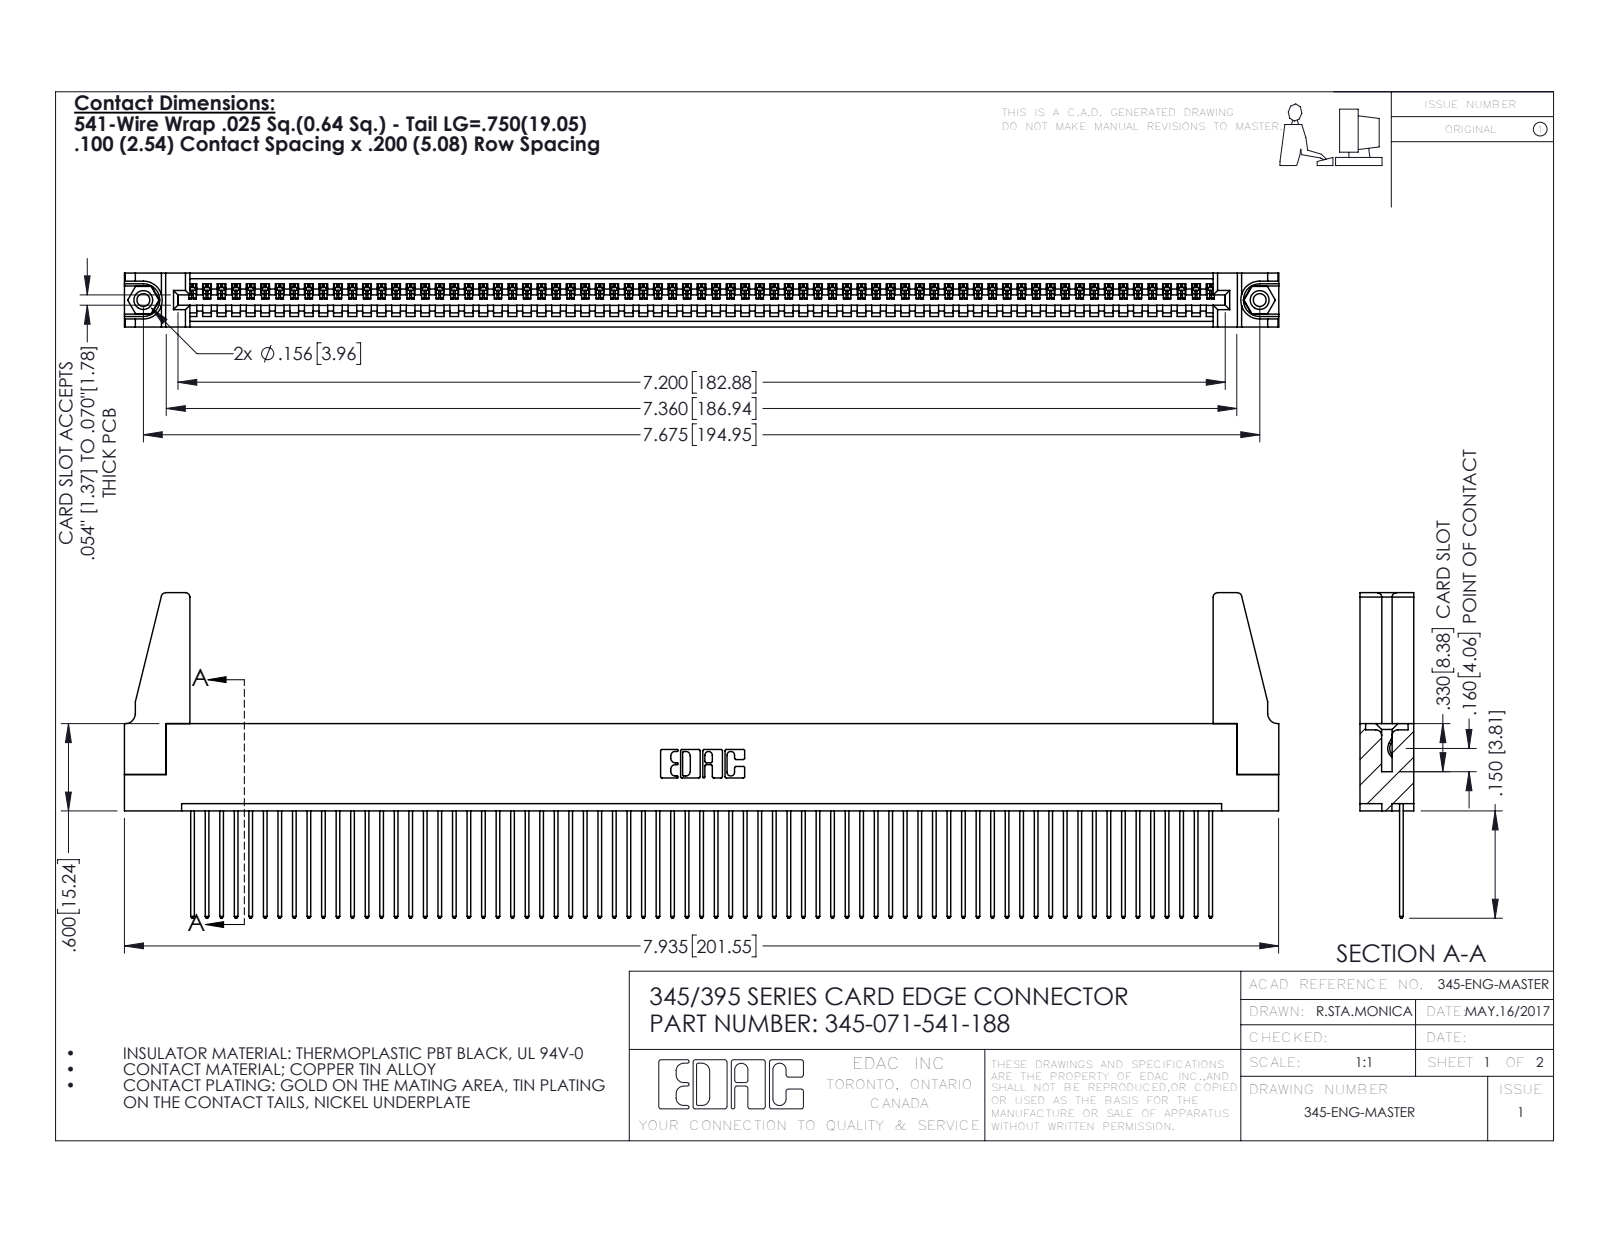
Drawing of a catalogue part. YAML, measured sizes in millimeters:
part_name: "345-071-541-188; 345 Part_Flush Mounting Lugs - 0.156 Dia-TH; 345-250-001_345-250-001-102; 345-292-001_345-293-141 (+1 more)"
step_written_by: "SolidWorks 2016 (CONFIG_CONTROL_DESIGN)"
units: millimeters
bodies: {solids: 76, faces: 4368, planar: 2992, cylindrical: 1360, other: 16}
overall_size: [201.6, 56.8, 9.4]
volume: 22880
surface_area: 30970
round_holes:
  - {diameter: 2.3, count: 2}
  - {diameter: 3.2, count: 2}
  - {diameter: 4, count: 2}
  - {diameter: 1.6, count: 1}
round_bosses_or_shafts:
  - {diameter: 3.9, count: 2}
partial_cylinders:
  - {radius: 0.2, count: 142}
  - {radius: 0.3, count: 142}
  - {radius: 0.3, count: 22}
  - {radius: 0.8, count: 8}
  - {radius: 0.2, count: 6}
  - {radius: 0.8, count: 6}
  - {radius: 0.7, count: 3}
  - {radius: 0.8, count: 2}
face_to_face_distances: [1.8, 7.6, 9.4, 2.5, 6.9, 0.6, 5.1, 5.7, 3.8, 1.8]
hole_center_spacings: [6.9, 189, 194.9]
